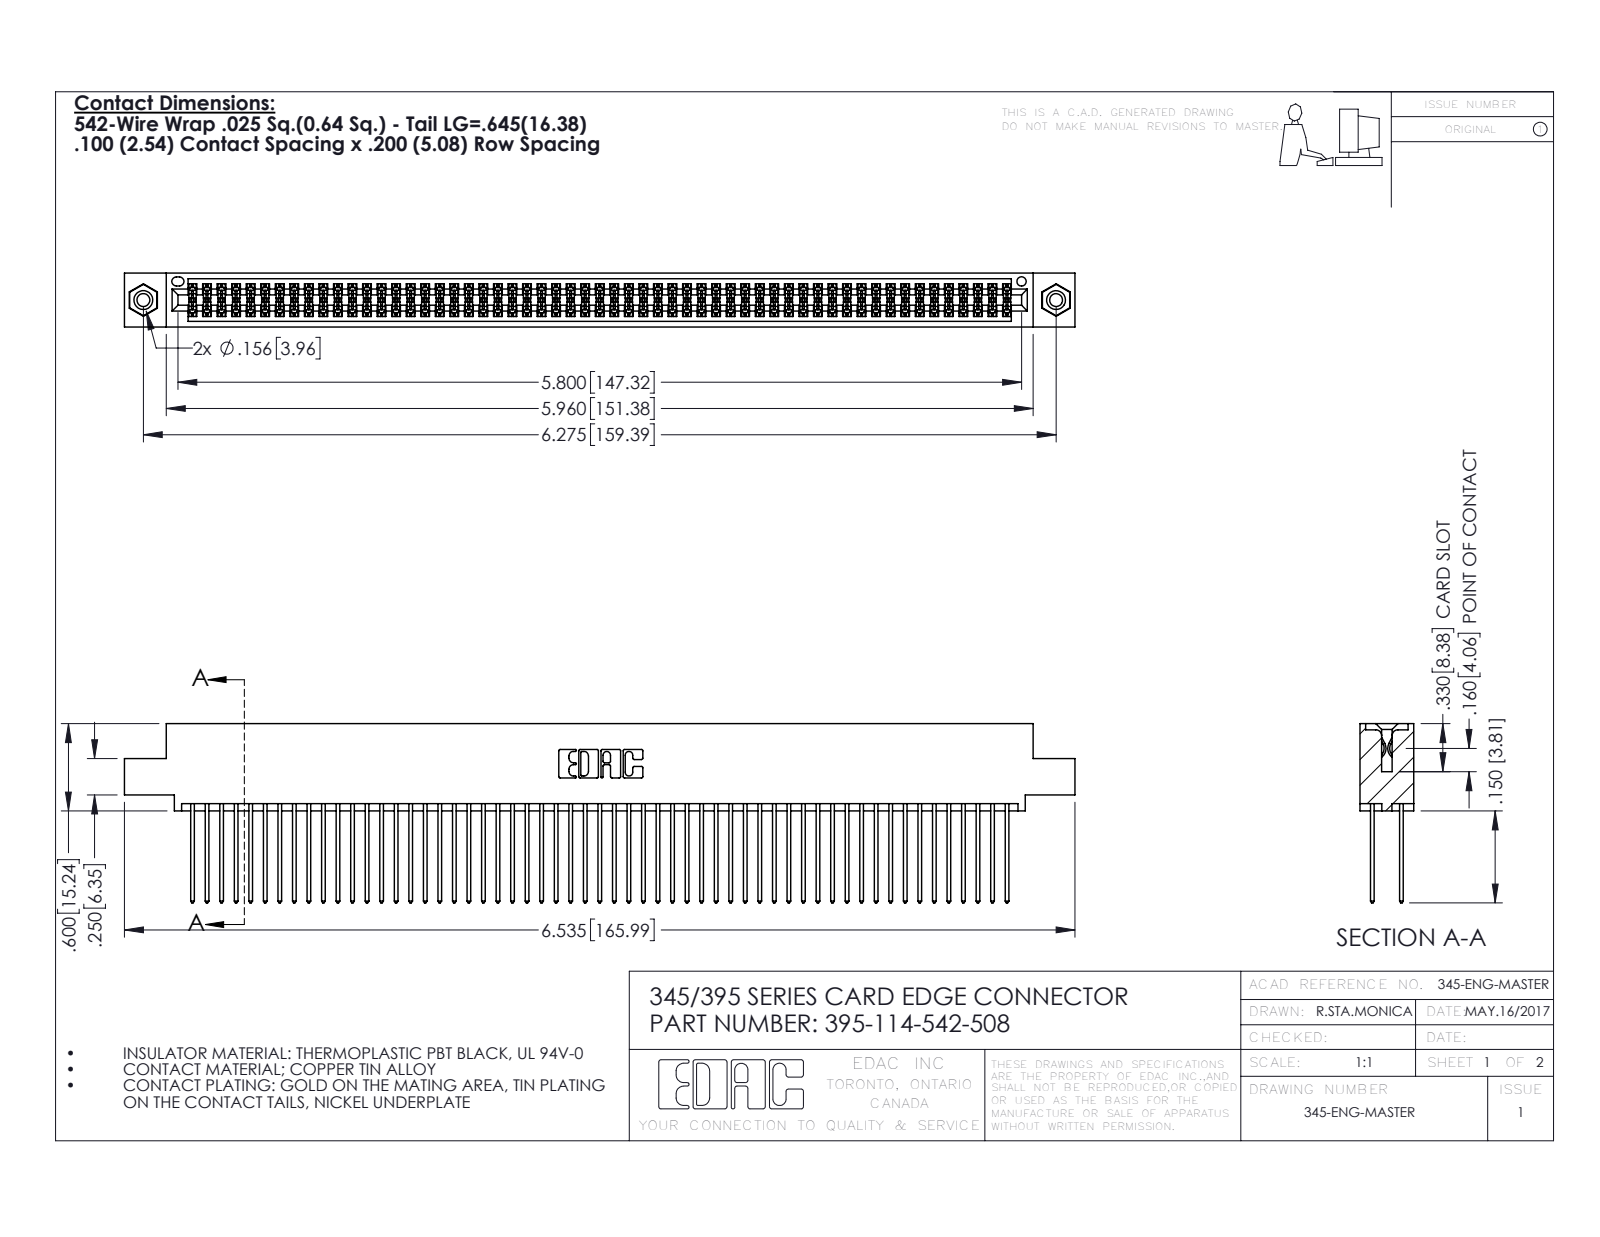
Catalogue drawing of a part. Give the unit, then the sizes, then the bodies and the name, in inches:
Units: inches
Overall size (bounding box): 6.535 × 1.232 × 0.37
Round holes (diameter × count): ⌀0.089 ×2, ⌀0.125 ×2, ⌀0.156 ×2, ⌀0.064 ×1
Round bosses / shafts (diameter × count): ⌀0.155 ×2
Partial cylindrical surfaces — rounded edges, fillets, slot ends (radius × count): R0.006 ×171, R0.01 ×114, R0.01 ×22, R0.007 ×6, R0.031 ×6, R0.026 ×3, R0.014 ×2, R0.019 ×2
Main face-to-face distances: 0.072, 0.298, 0.2, 0.098, 0.272, 0.025, 0.225, 0.37, 0.175, 0.149
Hole centre spacings: 0.27, 6.039, 6.275
Volume: 1.02 in³ · Surface area: 42.76 in²
Bodies: 117 solids, 5890 faces (3878 planar, 1996 cylindrical, 16 other)
Part name (STEP PRODUCT): 345 Part_0.110 Offset - 0.156 Dia-TI; 345-250-001_345-250-003-102; 345-292-001_345-293-142; 395-114-542-508
STEP written by: SolidWorks 2016 (CONFIG_CONTROL_DESIGN)
